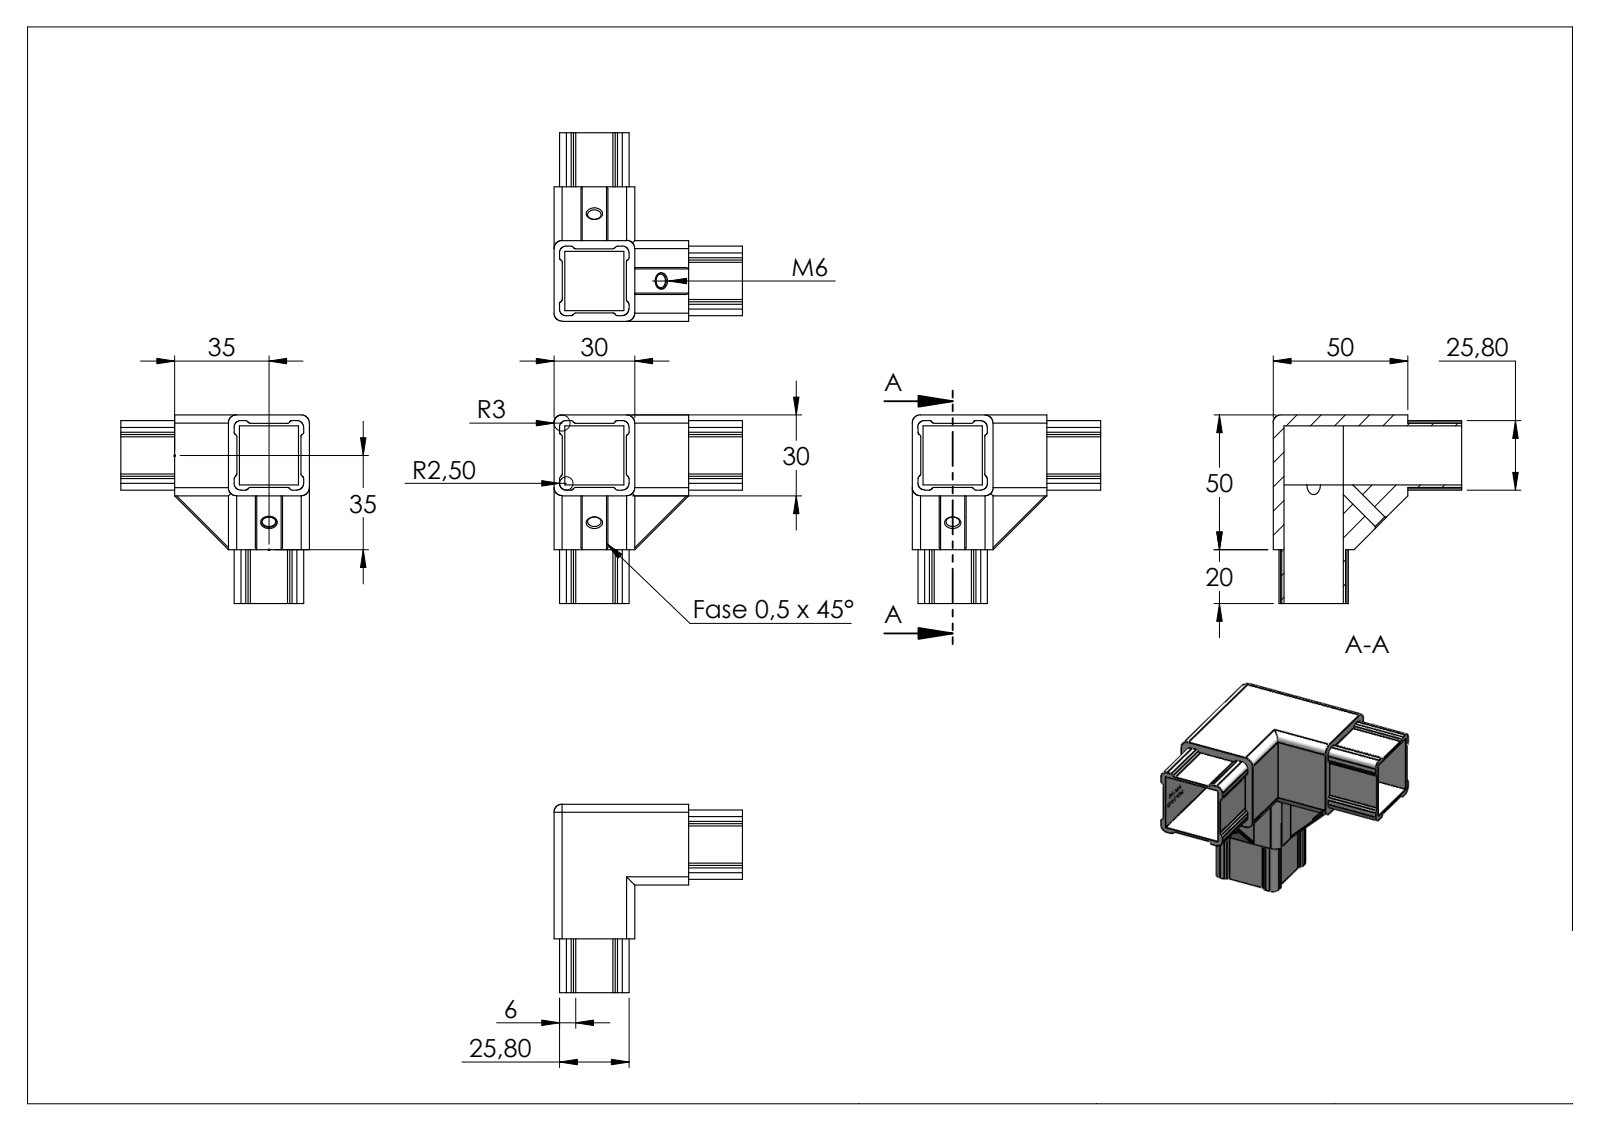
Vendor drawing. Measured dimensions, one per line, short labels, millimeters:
name: CR-VA30-03-S
written by: SolidWorks 2015 (CONFIG_CONTROL_DESIGN)
unit: mm
bodies: 1 solid, 410 faces (206 planar, 76 cylindrical, 128 other)
size: 70 × 70 × 70
volume: 44 956 mm³; area: 30 896 mm²
holes: 2× ⌀5
rounds: 48× R1, 12× R2.5, 12× R3
face distances: 4, 26, 22, 0.9, 3.1, 26.9, 22.9, 30, 20, 23.8
